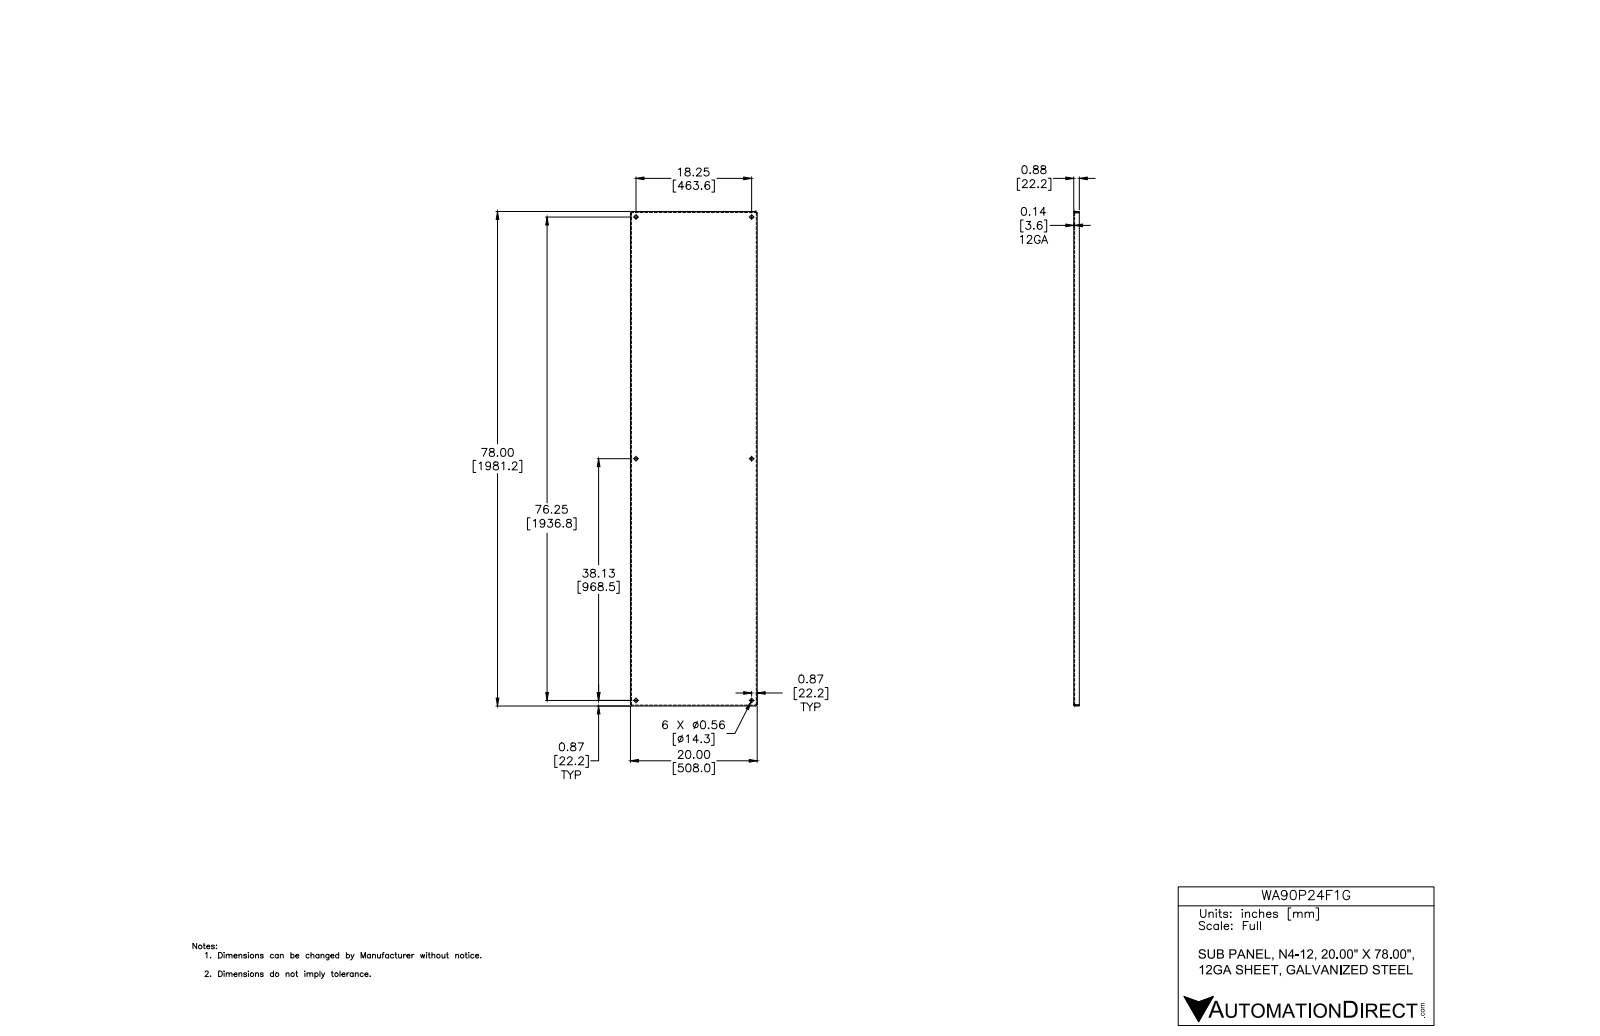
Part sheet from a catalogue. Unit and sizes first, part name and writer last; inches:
Units: inches
Overall size (bounding box): 78 × 20 × 0.875
Round holes (diameter × count): ⌀0.563 ×6
Partial cylindrical surfaces — rounded edges, fillets, slot ends (radius × count): R0.016 ×4, R0.109 ×4
Main face-to-face distances: 0.094, 19.906, 20, 19.813, 77.906, 0.781, 0.875, 78, 77.813, 0.16
Hole centre spacings: 18.25, 38.125, 38.125, 42.268, 42.268, 76.25, 78.404
Volume: 159.9 in³ · Surface area: 3 431 in²
Bodies: 1 solid, 44 faces (22 planar, 14 cylindrical, 8 other)
Part name (STEP PRODUCT): WA_P_F_G
STEP written by: Autodesk Inventor 2012 (AUTOMOTIVE_DESIGN)
